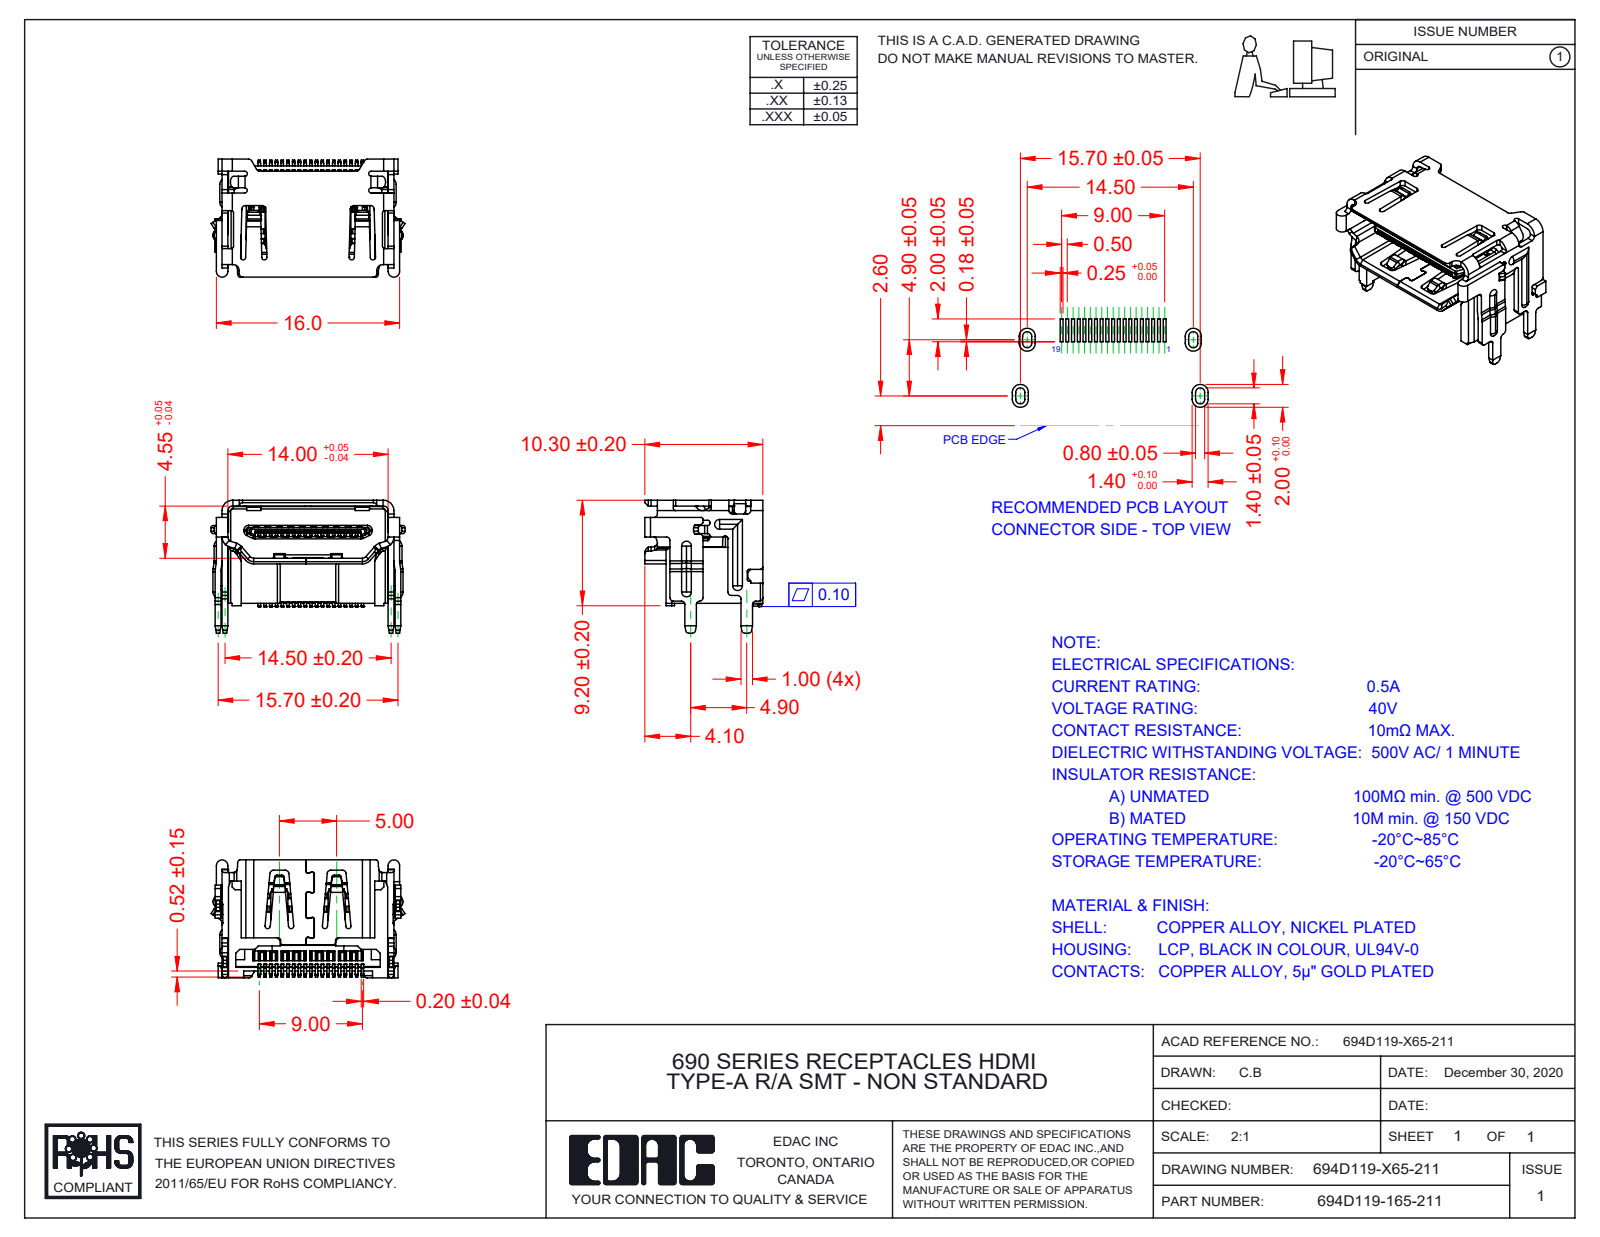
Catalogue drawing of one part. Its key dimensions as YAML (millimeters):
part_name: "Shell 694D119-X65-211; 694D119-165-211; Insulator 694D119-X65-211"
step_written_by: "SolidWorks 2020 (AUTOMOTIVE_DESIGN)"
units: millimeters
bodies: {solids: 2, faces: 2616, planar: 1649, cylindrical: 776, other: 191}
overall_size: [16.93, 11.6, 10.3]
volume: 494
surface_area: 1800
partial_cylinders:
  - {radius: 0.2, count: 123}
  - {radius: 0.3, count: 40}
  - {radius: 0.5, count: 28}
  - {radius: 0.15, count: 22}
  - {radius: 0.55, count: 22}
  - {radius: 0.23, count: 11}
  - {radius: 0.17, count: 8}
  - {radius: 0.4, count: 7}
face_to_face_distances: [0.5, 1, 0.55, 1.15, 13.95, 0.9, 2, 0.6, 14.45, 14.5]
